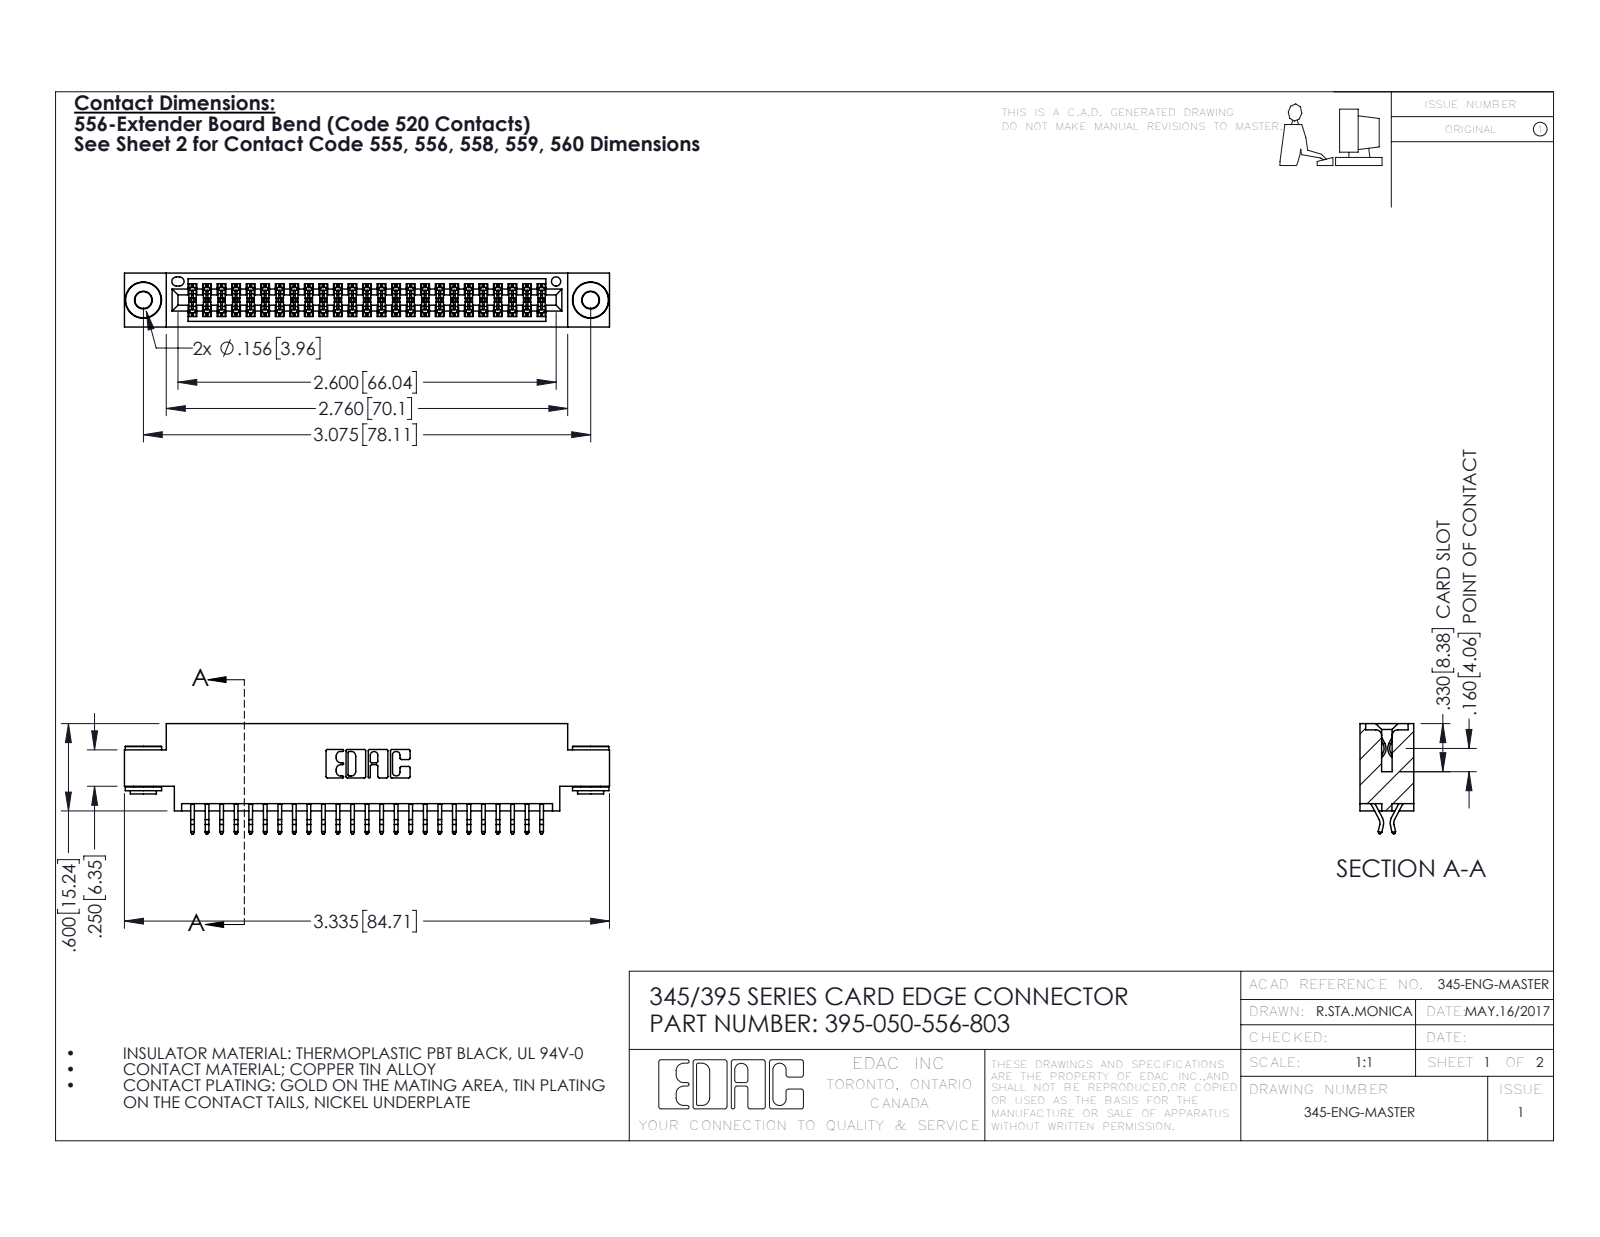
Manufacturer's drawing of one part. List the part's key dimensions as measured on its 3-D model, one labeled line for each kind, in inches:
Part name (STEP PRODUCT): 345-250-002_345-250-002-102; 345-292-001_556 Tail; 395-050-556-803; 345 Part_0.170 Offset - 0.156 Dia-TH
STEP written by: SolidWorks 2016 (CONFIG_CONTROL_DESIGN)
Units: inches
Bodies: 53 solids, 2968 faces (1944 planar, 1016 cylindrical, 8 other)
Overall size (bounding box): 3.335 × 0.757 × 0.37
Volume: 0.487 in³ · Surface area: 18.23 in²
Round holes (diameter × count): ⌀0.116 ×2, ⌀0.156 ×2, ⌀0.064 ×1
Round bosses / shafts (diameter × count): ⌀0.25 ×2, ⌀0.18 ×2, ⌀0.136 ×2
Partial cylindrical surfaces — rounded edges, fillets, slot ends (radius × count): R0.006 ×75, R0.01 ×22, R0.007 ×6, R0.031 ×6, R0.026 ×3, R0.01 ×2, R0.014 ×2, R0.019 ×2
Main face-to-face distances: 0.072, 0.298, 0.37, 0.2, 0.025, 0.098, 0.272, 0.225, 0.175, 0.149
Hole centre spacings: 0.27, 2.84, 3.075
